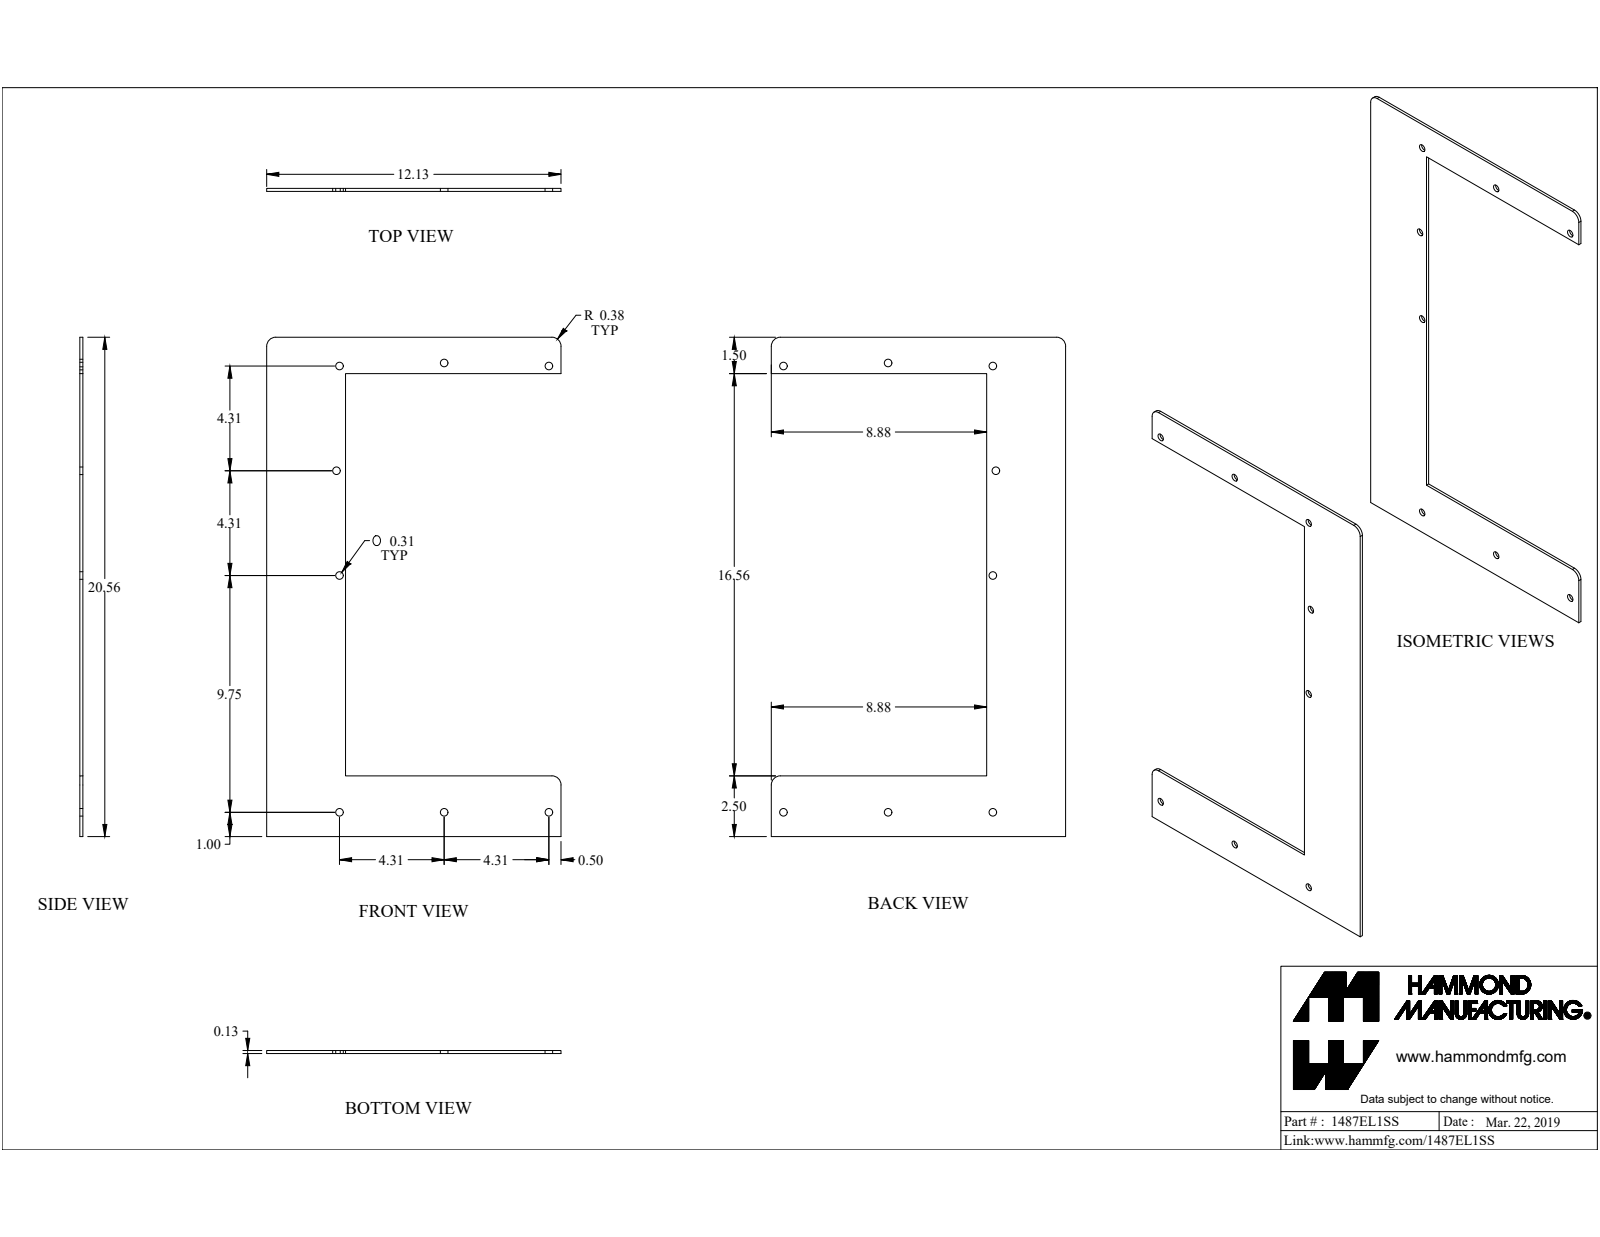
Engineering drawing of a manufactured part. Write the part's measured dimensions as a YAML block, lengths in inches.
part_name: "1487EL1SS"
step_written_by: "SolidWorks 2019 (CONFIG_CONTROL_DESIGN)"
units: inches
bodies: {solids: 6, faces: 226, planar: 144, cylindrical: 47, other: 35}
overall_size: [20.813, 14.125, 2.971]
volume: 13.2
surface_area: 239.2
round_holes:
  - {diameter: 0.313, count: 8}
  - {diameter: 0.196, count: 1}
  - {diameter: 0.258, count: 1}
  - {diameter: 0.35, count: 1}
round_bosses_or_shafts:
  - {diameter: 0.5, count: 1}
  - {diameter: 0.25, count: 1}
partial_cylinders:
  - {radius: 0.375, count: 7}
  - {radius: 0.02, count: 6}
  - {radius: 0.25, count: 1}
face_to_face_distances: [0.125, 0.03, 3.25, 20.593, 20.563, 2.5, 1.5, 1.53, 19.063, 18.093]
hole_center_spacings: [4.315, 8.625, 18.375, 18.874, 18.996, 20.299, 3.226, 4.312]
